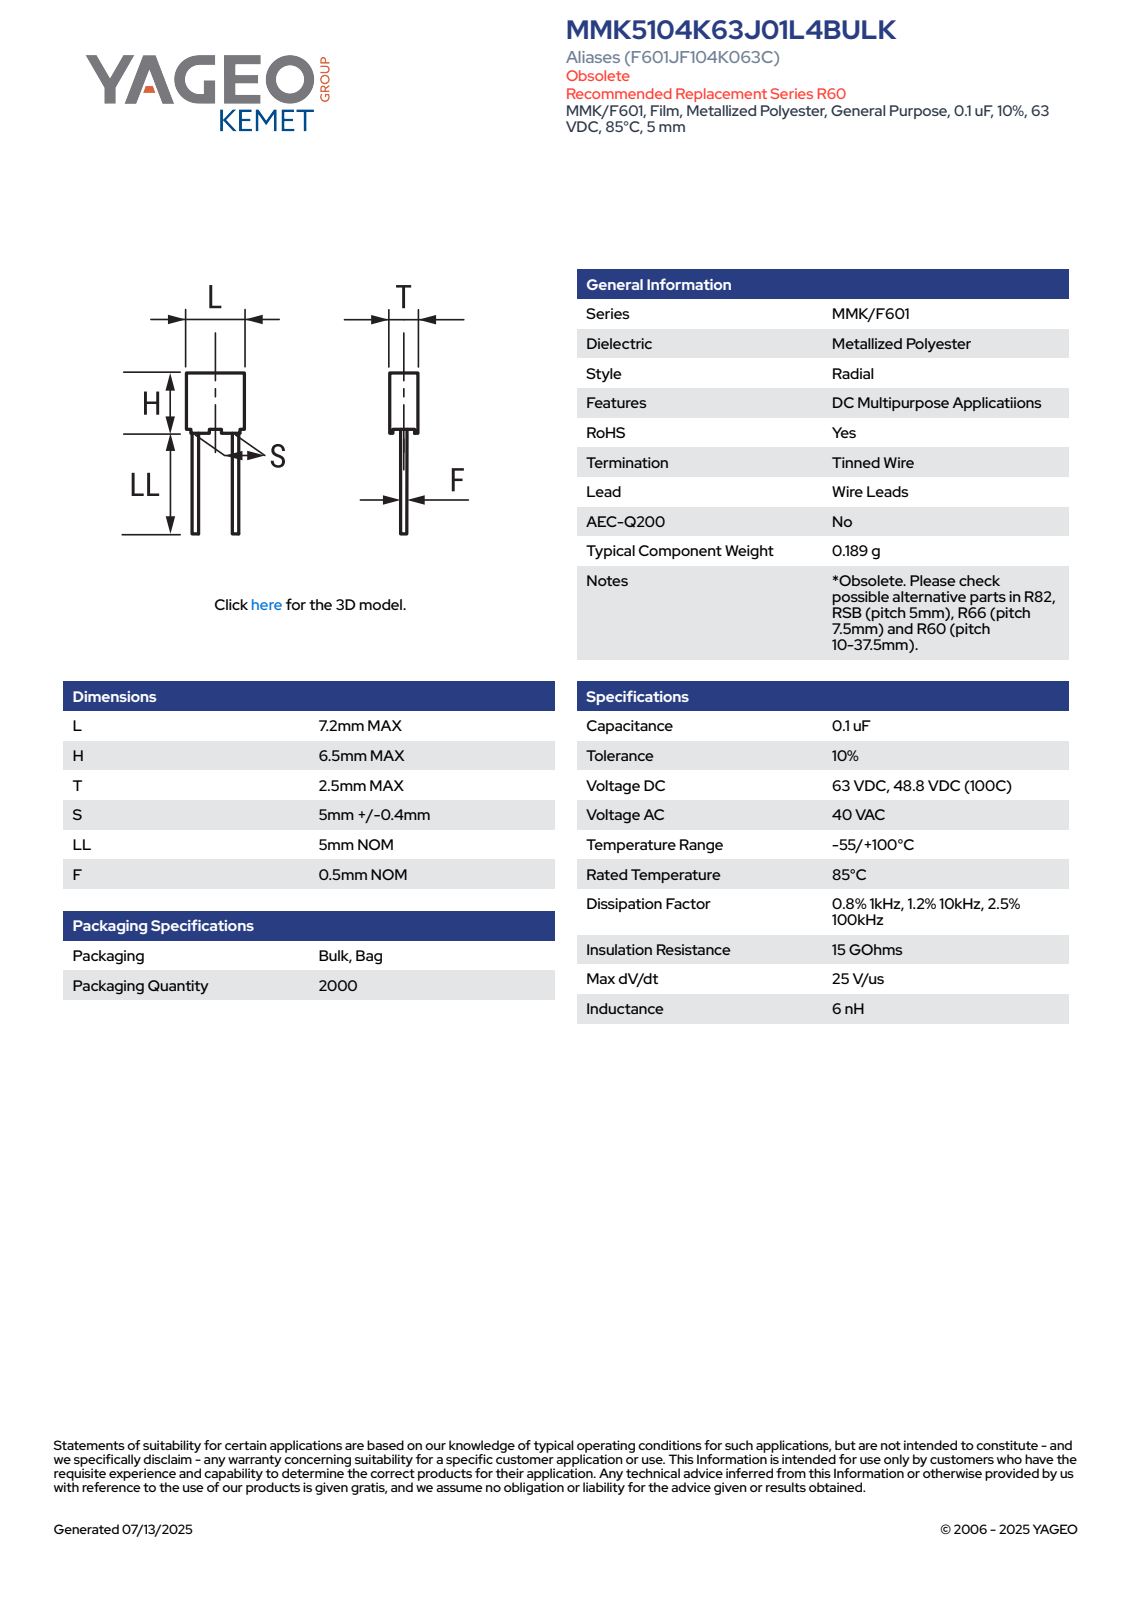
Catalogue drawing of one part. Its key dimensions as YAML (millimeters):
part_name: "CFR_RB3_7.2X6.5X2.5_L7.2H6.5T2.5S5LL5F0.5"
step_written_by: "SolidWorks 2014 (AUTOMOTIVE_DESIGN)"
units: millimeters
bodies: {solids: 4, faces: 85, planar: 77, cylindrical: 8, other: 0}
overall_size: [11.5, 7.2, 2.5]
volume: 108
surface_area: 191
round_bosses_or_shafts:
  - {diameter: 0.5, count: 2}
partial_cylinders:
  - {radius: 0.5, count: 4}
face_to_face_distances: [2.5, 7.2, 5.75, 2.26, 2.02, 0.75, 6.5, 6.96, 6.72, 0.53]
